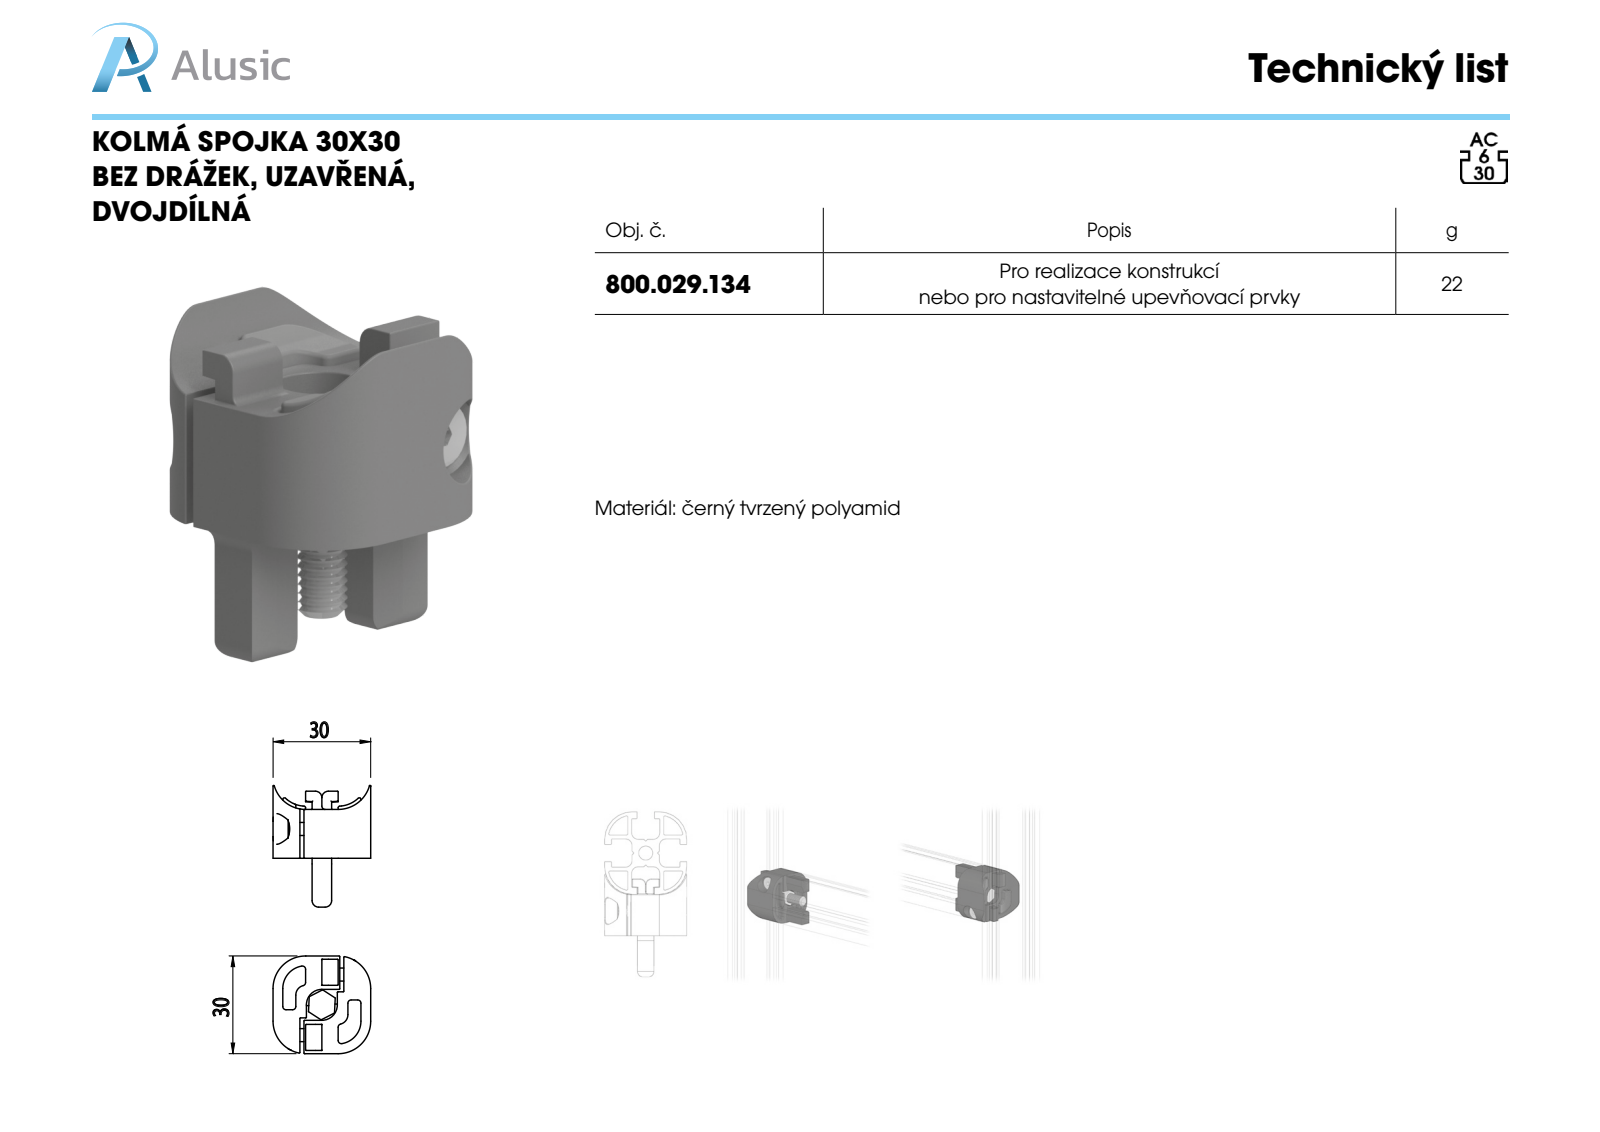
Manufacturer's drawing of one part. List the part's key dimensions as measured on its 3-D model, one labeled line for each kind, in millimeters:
Part name (STEP PRODUCT): 800.029.134; 800.029.134C; socket countersunk head screw_iso_ISO 10642 - M4 x 10 --- 10N; 800.029.134P (+1 more)
STEP written by: SolidWorks 2012 (CONFIG_CONTROL_DESIGN)
Units: millimetres
Bodies: 7 solids, 553 faces (161 planar, 202 cylindrical, 190 other)
Overall size (bounding box): 37.37 × 30 × 30
Volume: 12 860 mm³ · Surface area: 8 951 mm²
Round holes (diameter × count): ⌀4.5 ×2, ⌀6.3 ×2
Round bosses / shafts (diameter × count): ⌀7.53 ×2, ⌀4 ×2, ⌀6 ×1
Partial cylindrical surfaces — rounded edges, fillets, slot ends (radius × count): R0.2 ×54, R1 ×52, R2 ×10, R0.5 ×6, R10 ×6, R7 ×4, R3 ×2, R4.7 ×2
Main face-to-face distances: 3, 12, 15, 8, 1.25, 9, 18.75, 20, 2.5, 30
Hole centre spacings: 18.6
